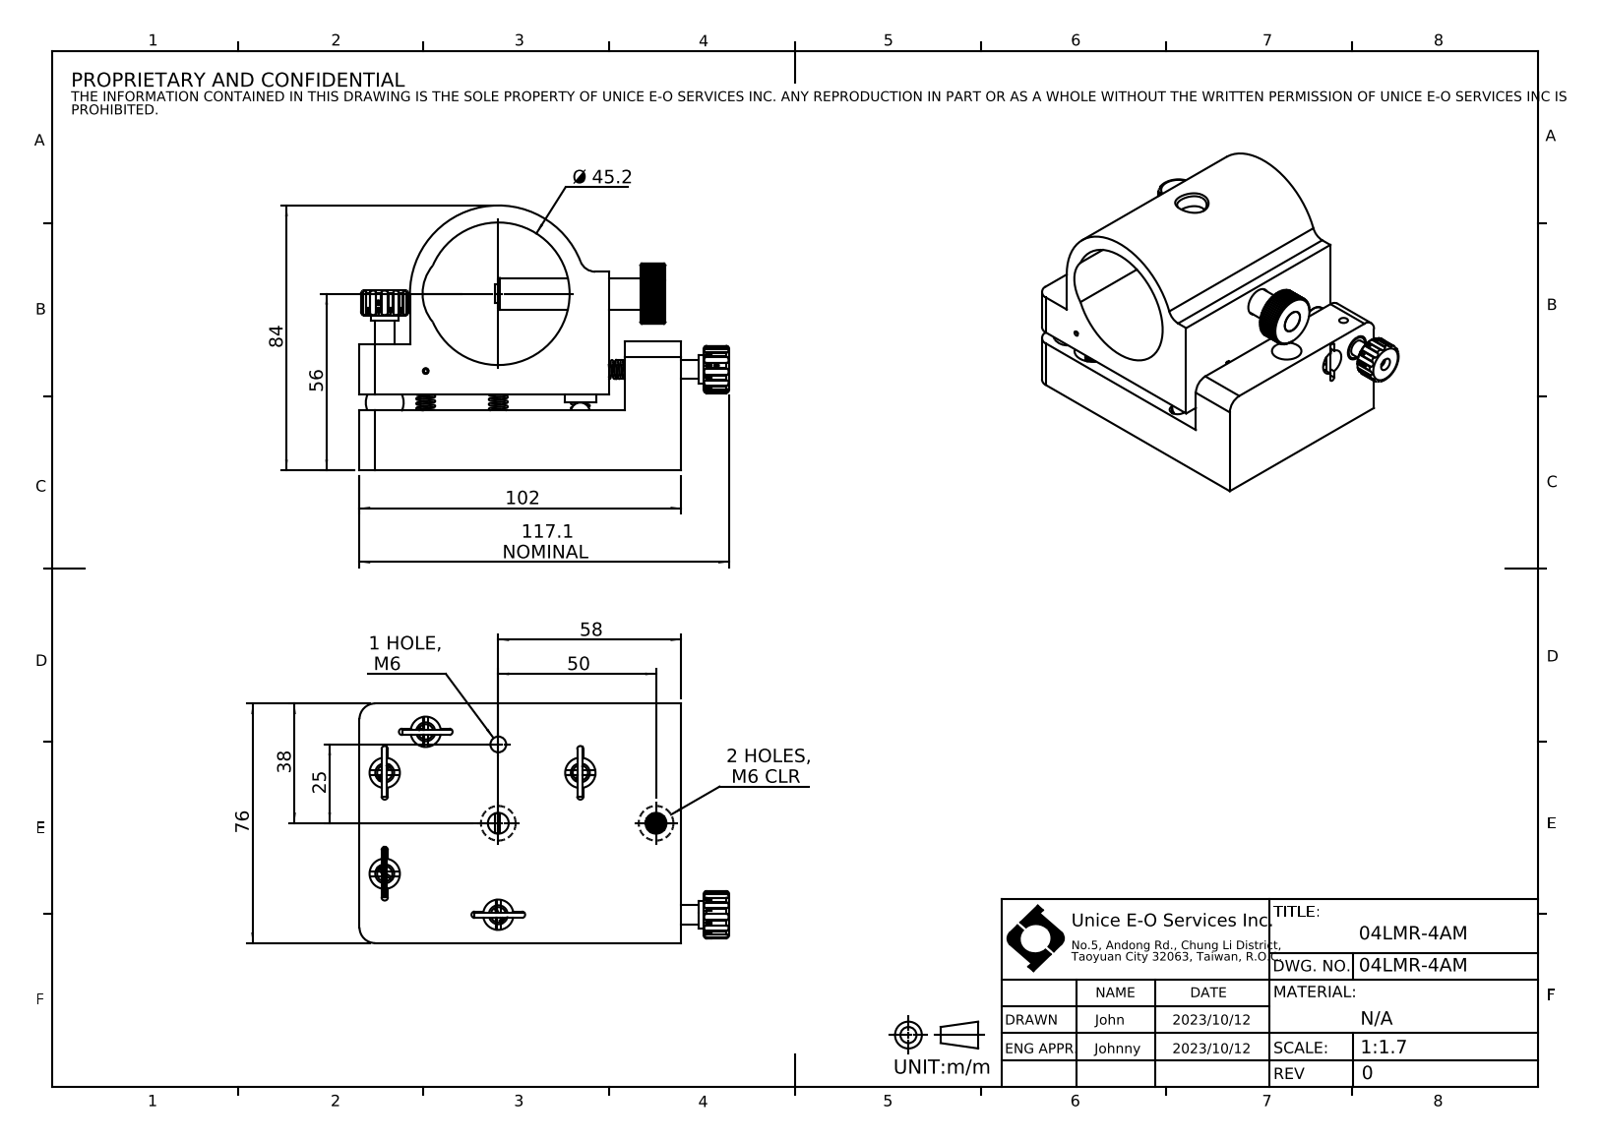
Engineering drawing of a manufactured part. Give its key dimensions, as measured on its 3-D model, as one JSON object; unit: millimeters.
{"part_name": "04LMR-4AM", "step_written_by": "SolidWorks 2016 (CONFIG_CONTROL_DESIGN)", "units": "millimeters", "bodies": {"solids": 35, "faces": 918, "planar": 275, "cylindrical": 482, "other": 161}, "overall_size": [117.13, 84, 76], "volume_mm3": 311185, "surface_area_mm2": 82973, "round_holes": [[1.2, 10], [9.6, 6], [1.8, 5], [2.5, 2], [3.3, 2], [4, 2], [4.7, 2], [5.95, 2], [6, 2], [6.6, 2], [9.5, 2], [11, 2]], "round_bosses_or_shafts": [[1.6, 10], [0.6, 7], [6, 3], [9, 2], [10, 1]], "partial_cylinders_radius": [[0.1, 72], [0.3, 48], [1.5, 24], [1, 12], [5, 5], [3, 4], [7.5, 2], [9.5, 1]], "face_to_face_distances": [5, 19, 24, 76, 23, 16, 102, 79, 63, 17.9], "hole_center_spacings": [13, 4, 13.6, 25.61, 28.84, 32, 32.14, 33.8]}
